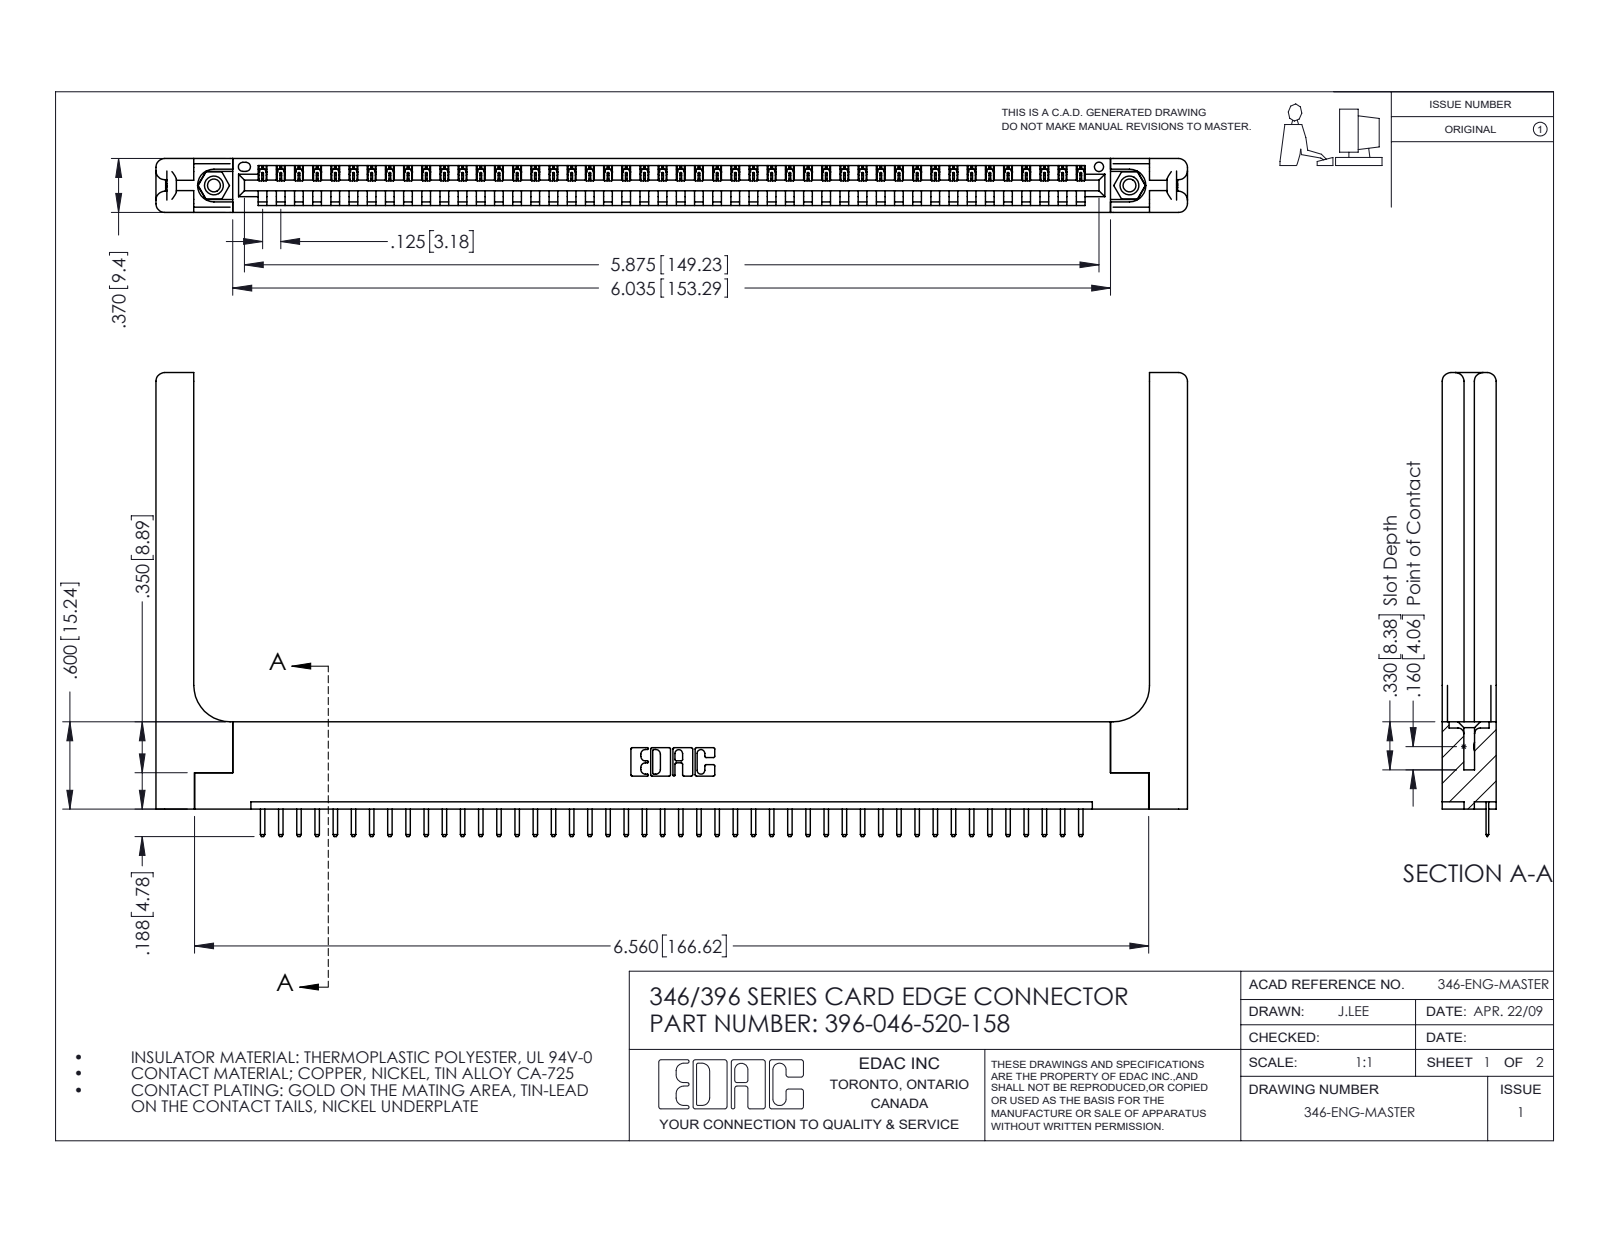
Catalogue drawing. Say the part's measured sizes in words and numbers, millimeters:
The part is named "346 Part_Flush Mounting Lugs - 0.156 Dia-TH; 345-292-001_345-293-120; 346-220-058_345-220-058; 396-046-520-158 (+1 more)". Its 3-D file was written by "SolidWorks 2016 (CONFIG_CONTROL_DESIGN)". It is 51 solids with 3230 faces: 2156 planar, 1014 cylindrical and 60 other. Overall it measures 180.1 by 81 by 9.4 millimeters. Its volume is 24 650 cubic millimeters and its surface area 26 190 square millimeters. Round holes: 2 of diameter 2.3, 2 of diameter 3.2, 2 of diameter 4, 1 of diameter 1.6. Round bosses or shafts: 2 of diameter 3.9. Partial cylindrical surfaces (rounded edges, fillets, slot ends): 94 of radius 0.3, 92 of radius 0.2, 22 of radius 0.3, 16 of radius 1.5, 6 of radius 0.2, 6 of radius 0.8, 3 of radius 0.7, 2 of radius 0.8. The main face-to-face distances are 9.4, 1.2, 8.2, 1.8, 3.8, 3.8, 6.4, 7.6, 0.6, 5.6. The hole center spacings are 6.2, 154.6, 159.9.
